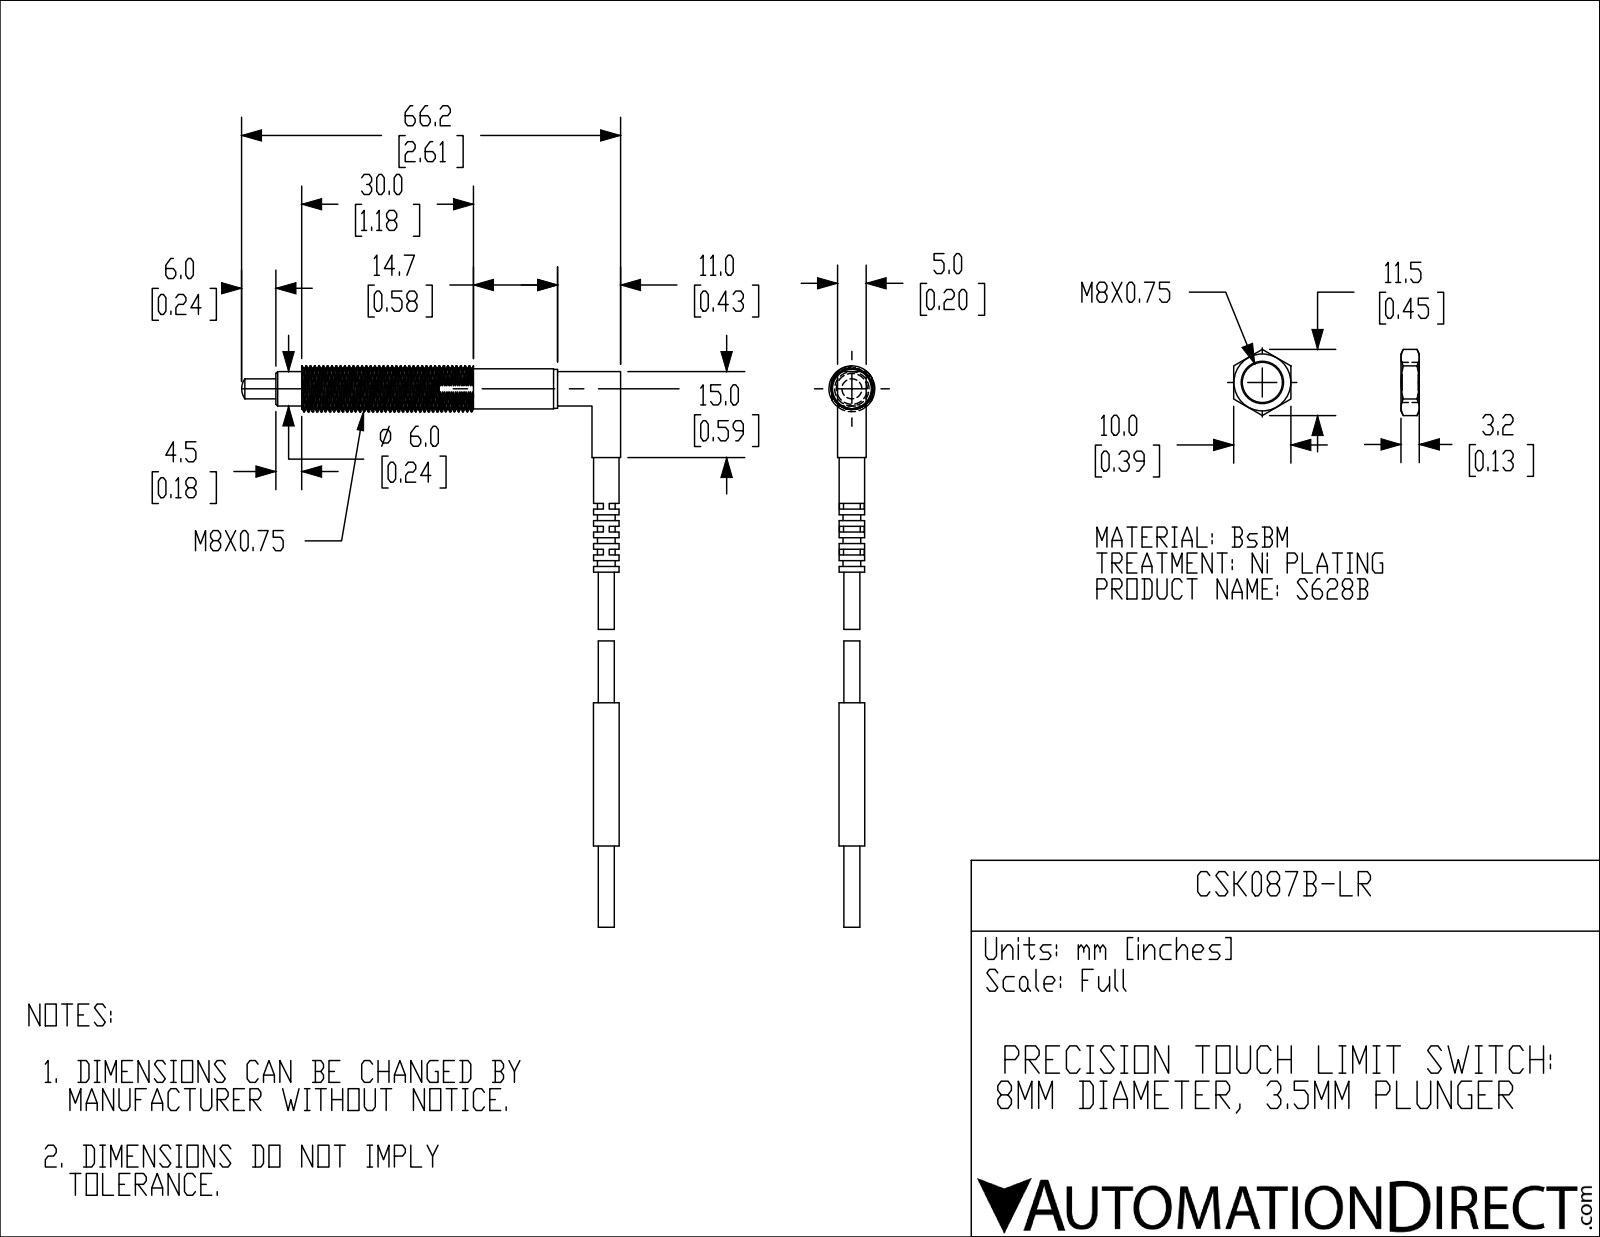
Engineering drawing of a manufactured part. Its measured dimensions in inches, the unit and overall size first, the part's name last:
Units: inches
Overall size (bounding box): 3.858 × 2.606 × 0.315
Round bosses / shafts (diameter × count): ⌀0.315 ×1, ⌀0.276 ×1, ⌀0.268 ×1, ⌀0.236 ×1, ⌀0.177 ×1, ⌀0.175 ×1, ⌀0.138 ×1, ⌀0.122 ×1
Main face-to-face distances: 0.197, 0.039, 0.236, 0.079, 0.118, 0.157, 0.276, 0.354, 0.315, 0.433
Volume: 0.224 in³ · Surface area: 4.317 in²
Bodies: 2 solids, 84 faces (60 planar, 22 cylindrical, 2 other)
Part name (STEP PRODUCT): CSK087B-LR
STEP written by: SolidWorks 2018 (AUTOMOTIVE_DESIGN)
